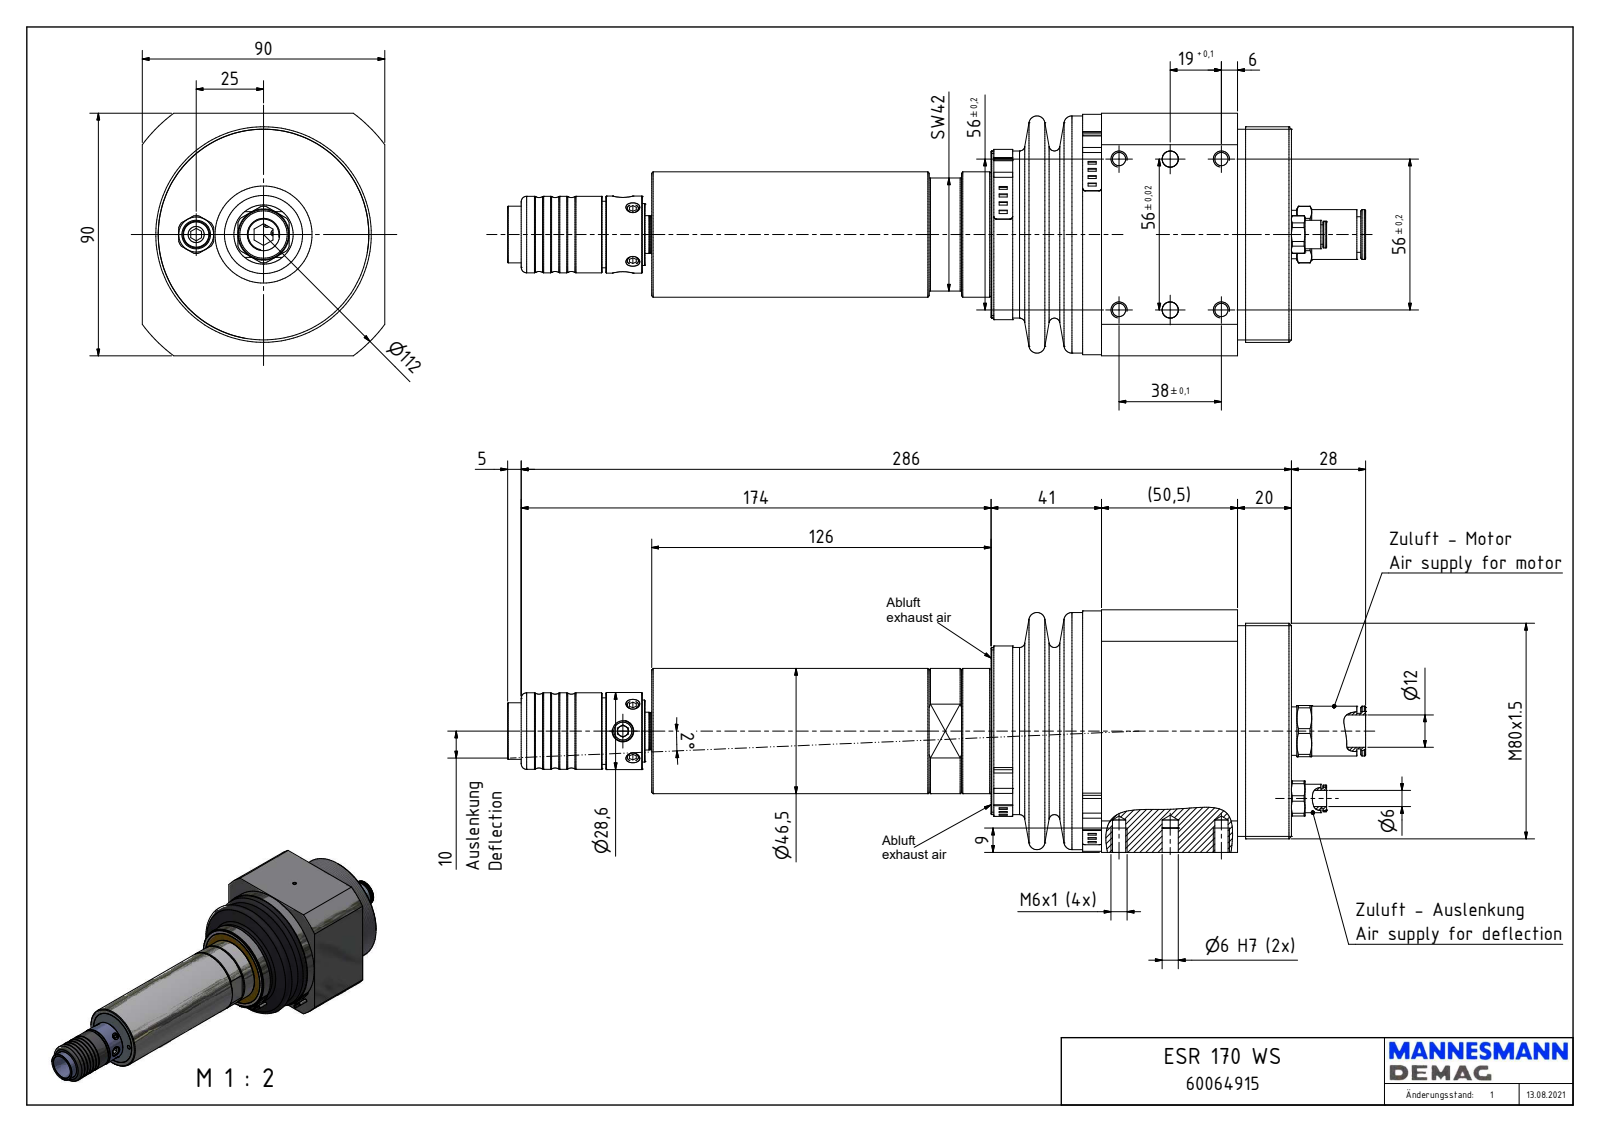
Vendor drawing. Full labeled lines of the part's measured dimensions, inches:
Part name (STEP PRODUCT): ESR 170 WS_60064915
STEP written by: Autodesk Inventor 2021 (AUTOMOTIVE_DESIGN)
Units: inches
Bodies: 1 solid, 380 faces (164 planar, 128 cylindrical, 88 other)
Overall size (bounding box): 12.541 × 3.543 × 3.543
Volume: 56.78 in³ · Surface area: 156.7 in²
Round holes (diameter × count): ⌀0.194 ×4, ⌀0.236 ×3, ⌀0.118 ×2, ⌀0.236 ×2, ⌀0.098 ×1, ⌀0.262 ×1, ⌀0.337 ×1, ⌀0.472 ×1, ⌀0.63 ×1, ⌀0.831 ×1, ⌀1.417 ×1, ⌀2.835 ×1
Round bosses / shafts (diameter × count): ⌀3.512 ×1, ⌀3.465 ×1, ⌀3.15 ×1, ⌀3.078 ×1, ⌀2.817 ×1, ⌀2.488 ×1, ⌀2.441 ×1, ⌀1.831 ×1
Partial cylindrical surfaces — rounded edges, fillets, slot ends (radius × count): R0.02 ×8, R0.039 ×8, R0.043 ×8, R0.055 ×4, R0.079 ×4, R0.081 ×2, R0.12 ×2, R0.276 ×1
Main face-to-face distances: 3.543, 0.787, 1.988, 2.776, 9.35, 6.575, 8.563, 1.614, 4.961, 3.602
Hole centre spacings: 0.748, 2.328, 2.205, 0.669, 1.104, 1.19, 1.3, 1.366
